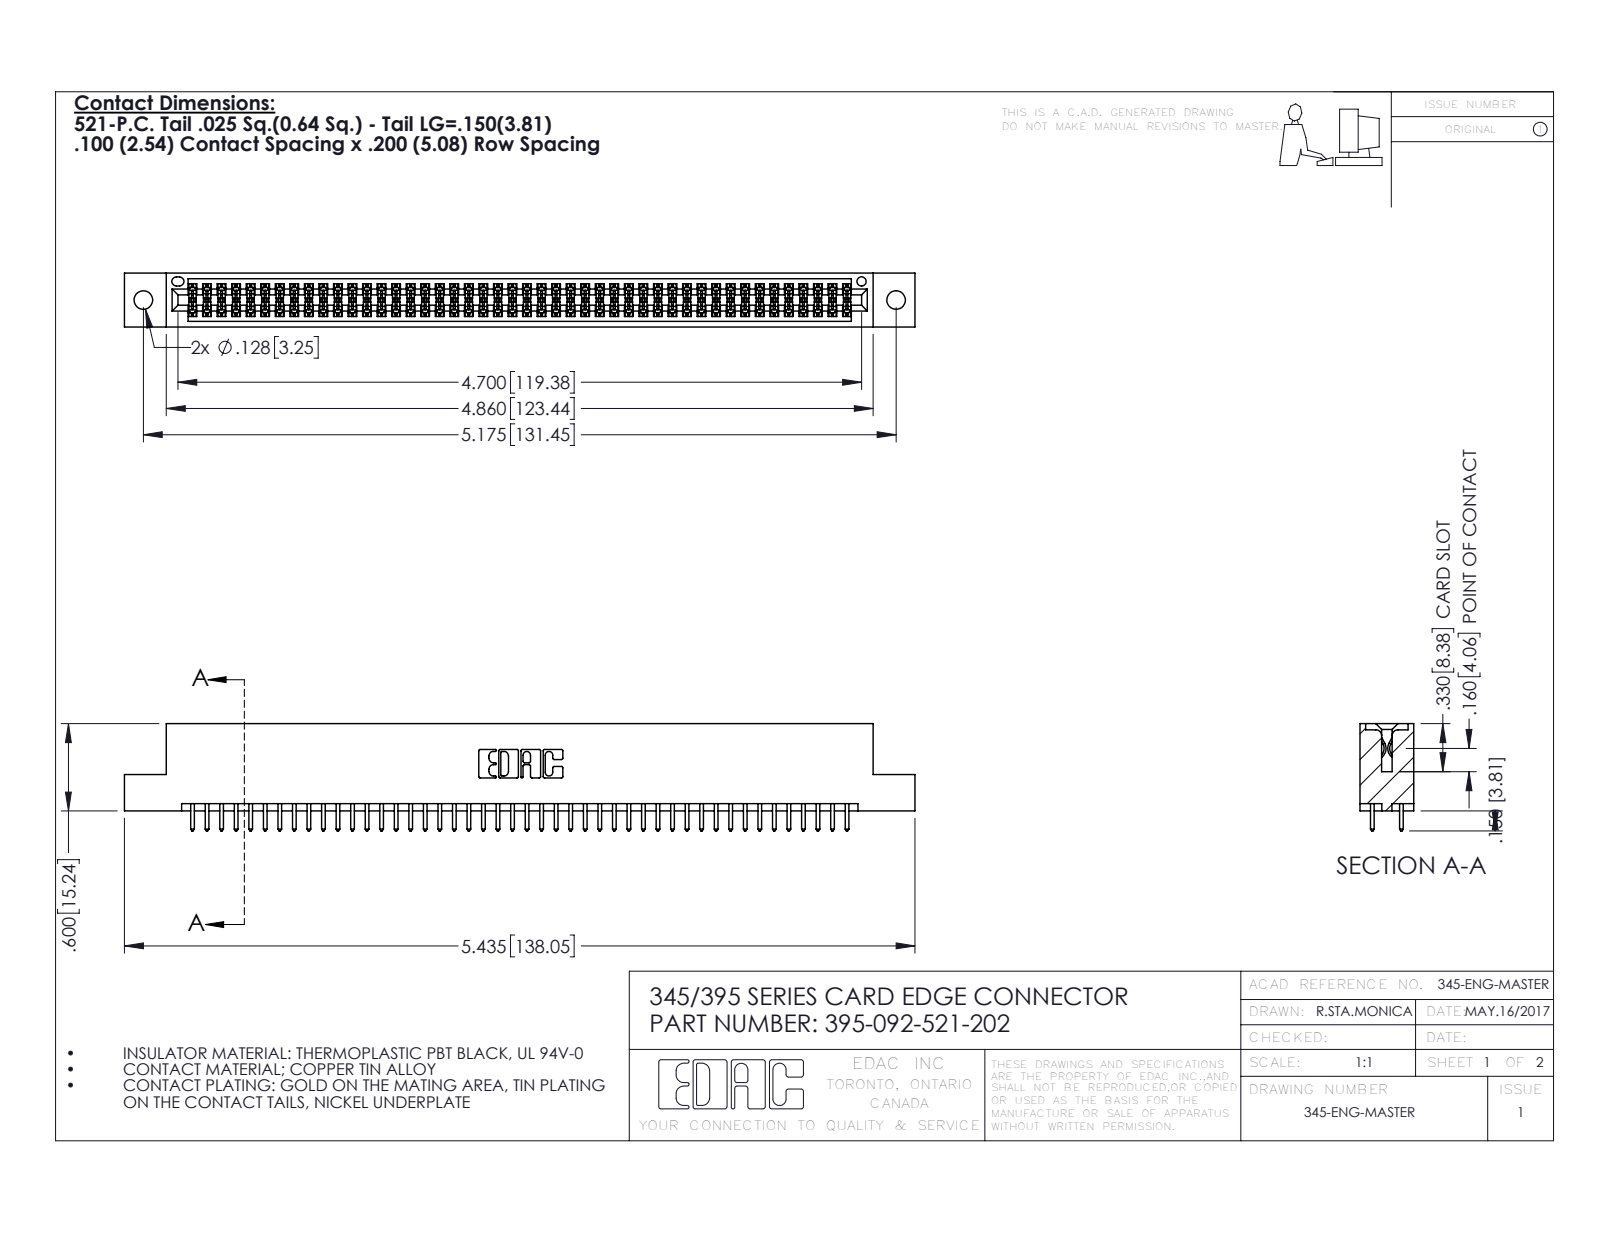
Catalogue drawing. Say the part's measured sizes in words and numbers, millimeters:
The part is named "345-292-001_345-293-121; 345 Part_Flush Mounting Lugs - 0.128 Dia; 395-092-521-202". Its 3-D file was written by "SolidWorks 2016 (CONFIG_CONTROL_DESIGN)". It is 93 solids with 4726 faces: 3116 planar, 1610 cylindrical and 0 other. Overall it measures 138 by 18.7 by 9.4 millimeters. Its volume is 13 400 cubic millimeters and its surface area 19 330 square millimeters. Round holes: 2 of diameter 3.3, 1 of diameter 1.6. Partial cylindrical surfaces (rounded edges, fillets, slot ends): 138 of radius 0.2, 92 of radius 0.3, 22 of radius 0.3, 6 of radius 0.2, 6 of radius 0.8, 3 of radius 0.7, 2 of radius 0.4, 2 of radius 0.5. The main face-to-face distances are 7.6, 1.8, 5.1, 9.4, 2.5, 6.9, 0.6, 5.7, 4.4, 3.8. The hole center spacings are 6.9, 125.5, 131.4.
